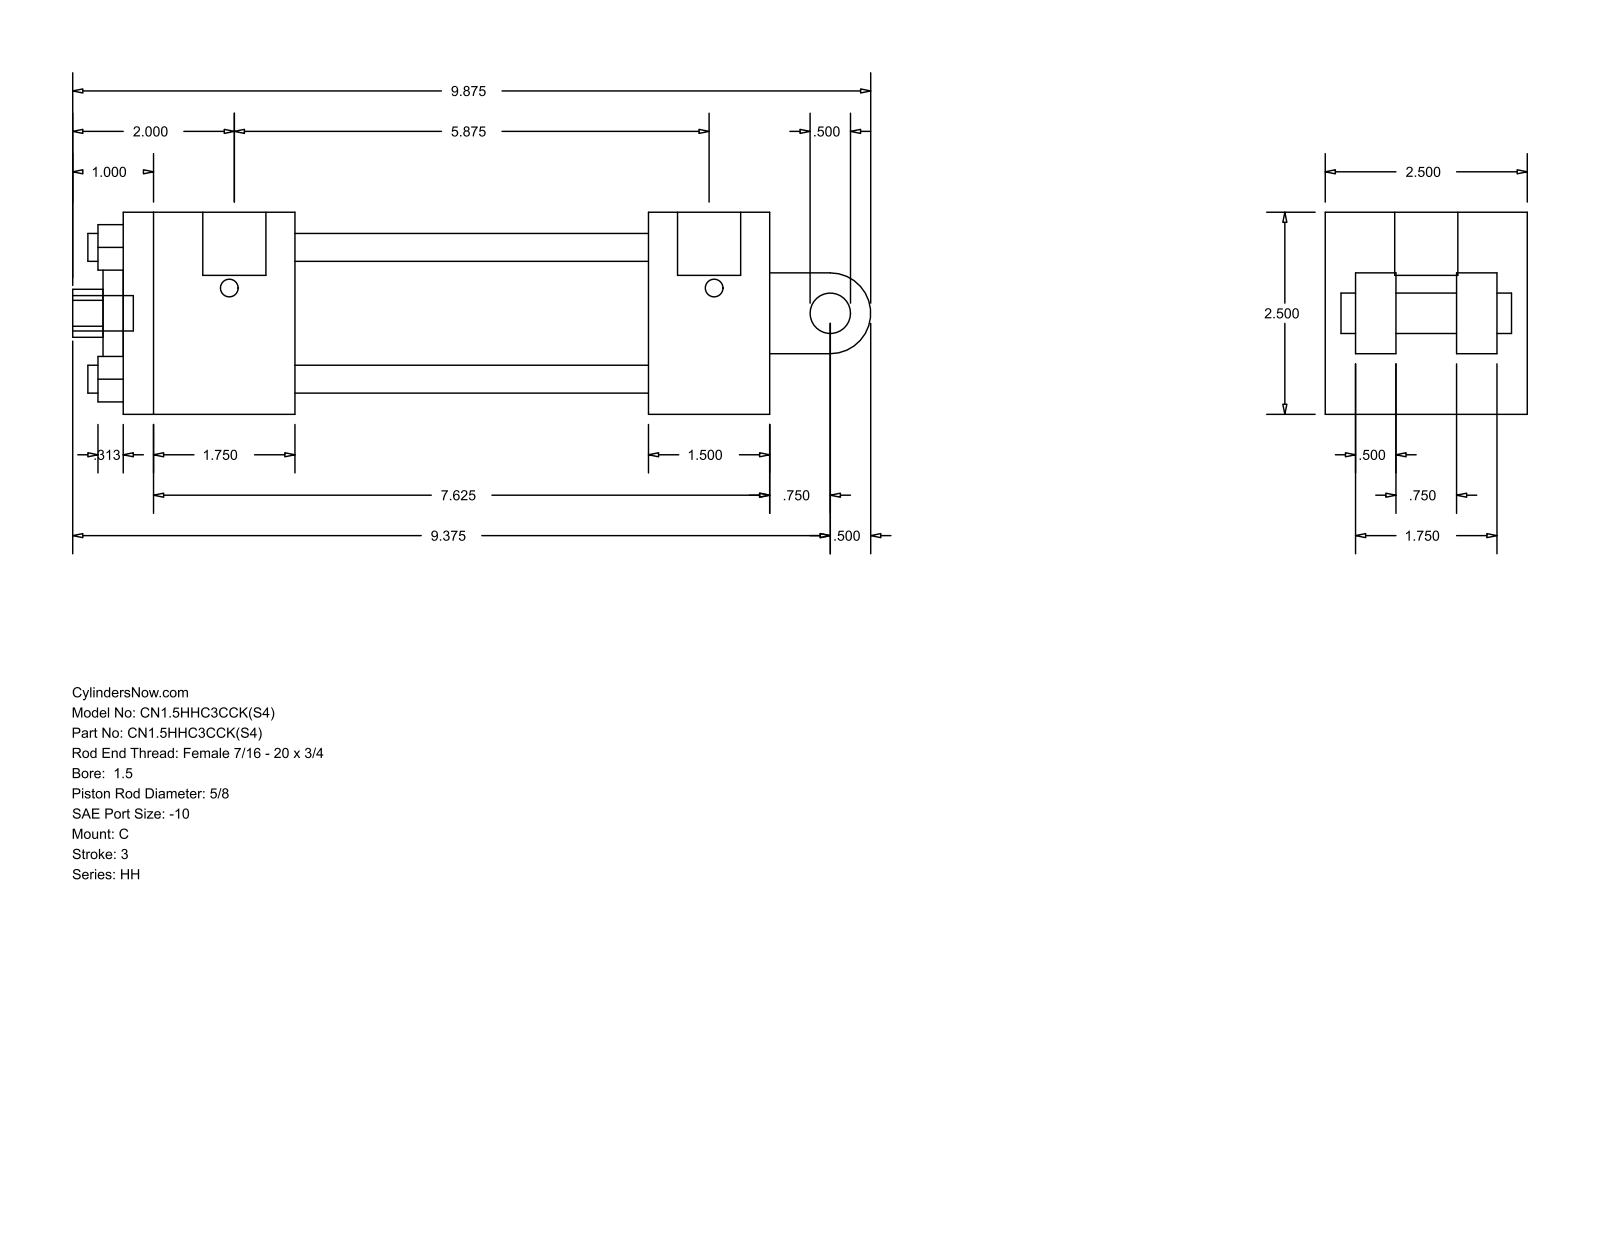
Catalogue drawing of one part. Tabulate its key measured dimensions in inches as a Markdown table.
| quantity | value |
| --- | --- |
| part name | HH_C__0150_0.625 |
| STEP written by | GSSL Pune (CONFIG_CONTROL_DESIGN) |
| units | inches |
| bodies | 0 solids, 99 faces (70 planar, 29 cylindrical, 0 other) |
| overall size | 9.875 × 2.5 × 2.5 |
| round holes (diameter × count) | 0.345 × 4, 0.219 × 2, 0.625 × 1, 0.781 × 1, 1.125 × 1, 1.75 × 1 |
| round bosses / shafts (diameter × count) | 0.219 × 2, 0.781 × 1, 0.5 × 1, 0.437 × 1 |
| partial cylindrical surfaces (radius × count) | 0.297 × 1, 0.5 × 1 |
| main face-to-face distances | 2.5, 8, 1.5, 2.125, 6.5, 4.375, 5.875, 0.5, 0.375, 0.75 |
| hole center spacings | 1.152, 1.63, 2.305, 0.062 |
